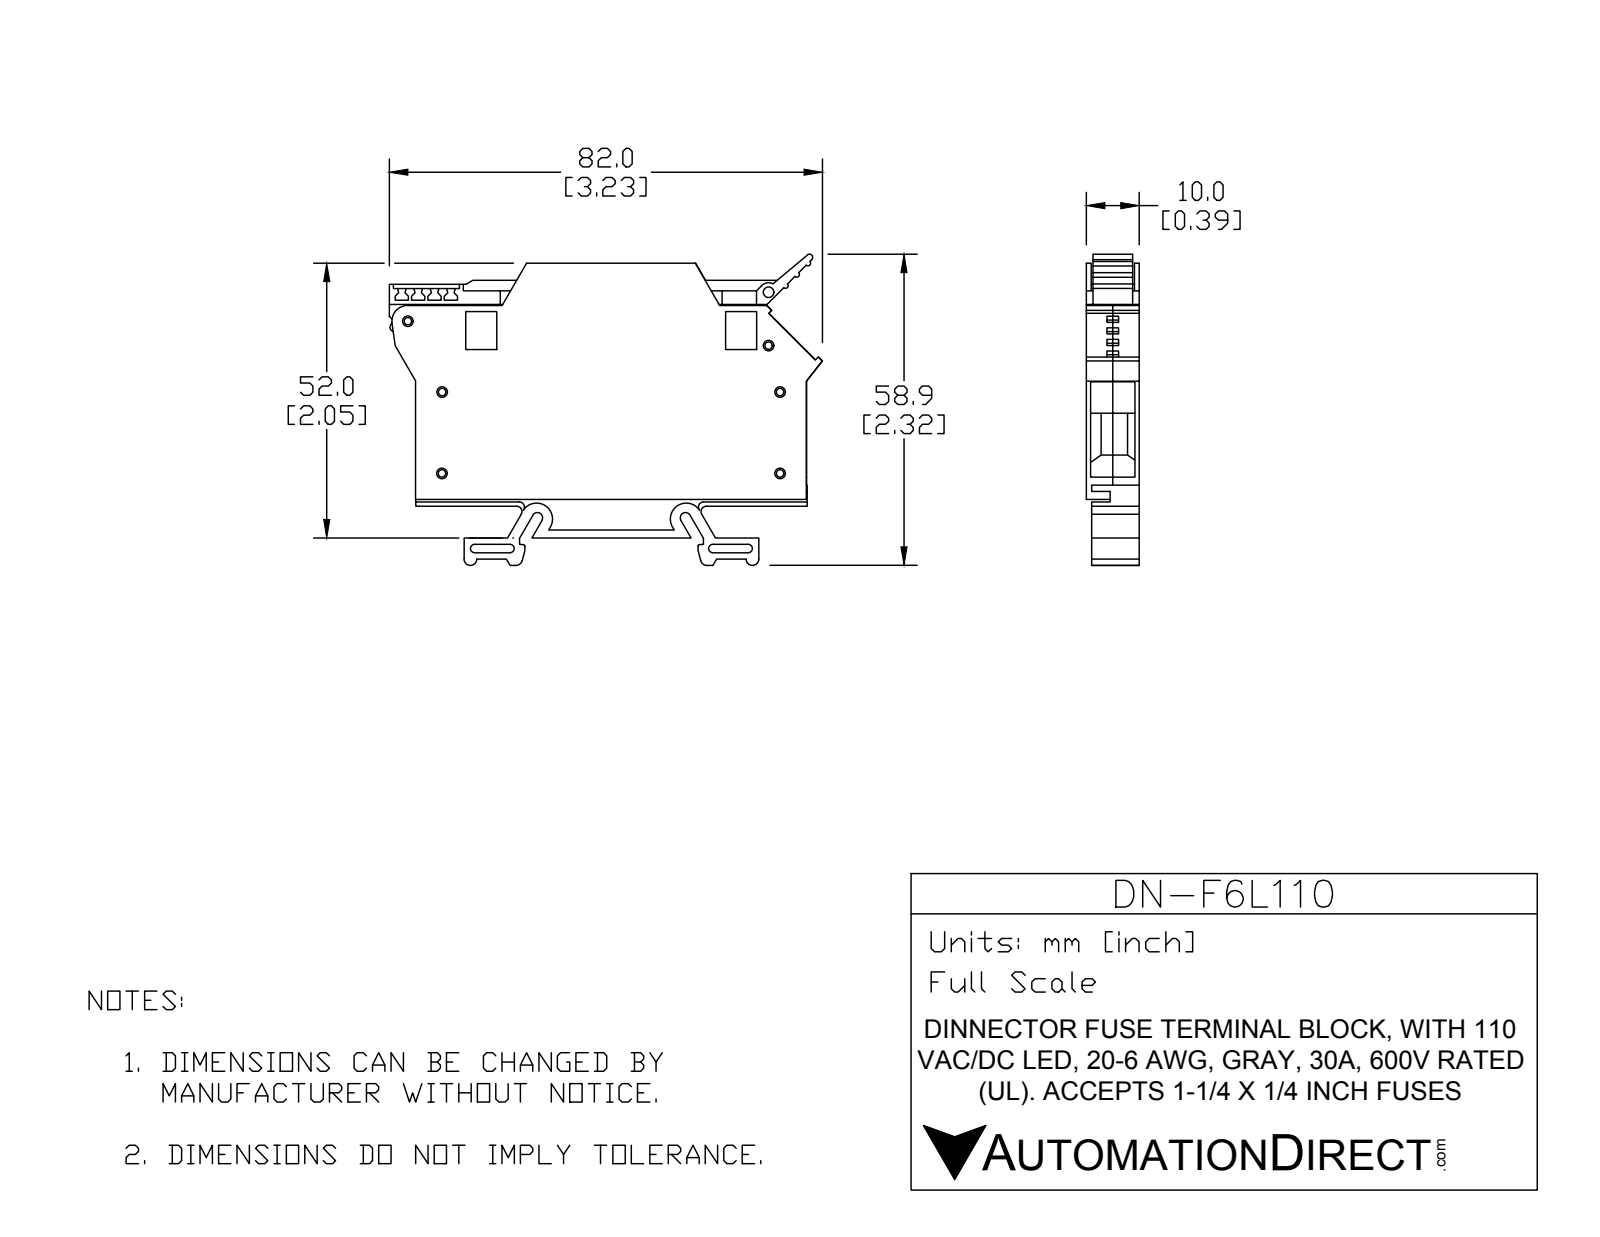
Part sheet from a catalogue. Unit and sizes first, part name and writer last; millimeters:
Units: millimetres
Overall size (bounding box): 82 × 58.9 × 10
Round holes (diameter × count): ⌀2 ×7, ⌀2.81 ×5, ⌀1.5 ×4, ⌀5.5 ×2, ⌀2.1 ×1
Partial cylindrical surfaces — rounded edges, fillets, slot ends (radius × count): R0.5 ×15, R3 ×7, R1 ×6, R2 ×5, R0.2 ×4, R0.8 ×4, R1.2 ×4, R4.2 ×4
Main face-to-face distances: 10, 2, 0.9, 1.5, 9.1, 3.5, 0.8, 8.5, 4, 0.5
Hole centre spacings: 15.4, 3, 18.2, 64, 65.83, 9.07, 9.81, 10.1
Volume: 27 591 mm³ · Surface area: 17 815 mm²
Bodies: 1 solid, 604 faces (412 planar, 141 cylindrical, 51 other)
Part name (STEP PRODUCT): 43480H_DN-F624; 20753H
STEP written by: SolidWorks 2013 (AUTOMOTIVE_DESIGN)
